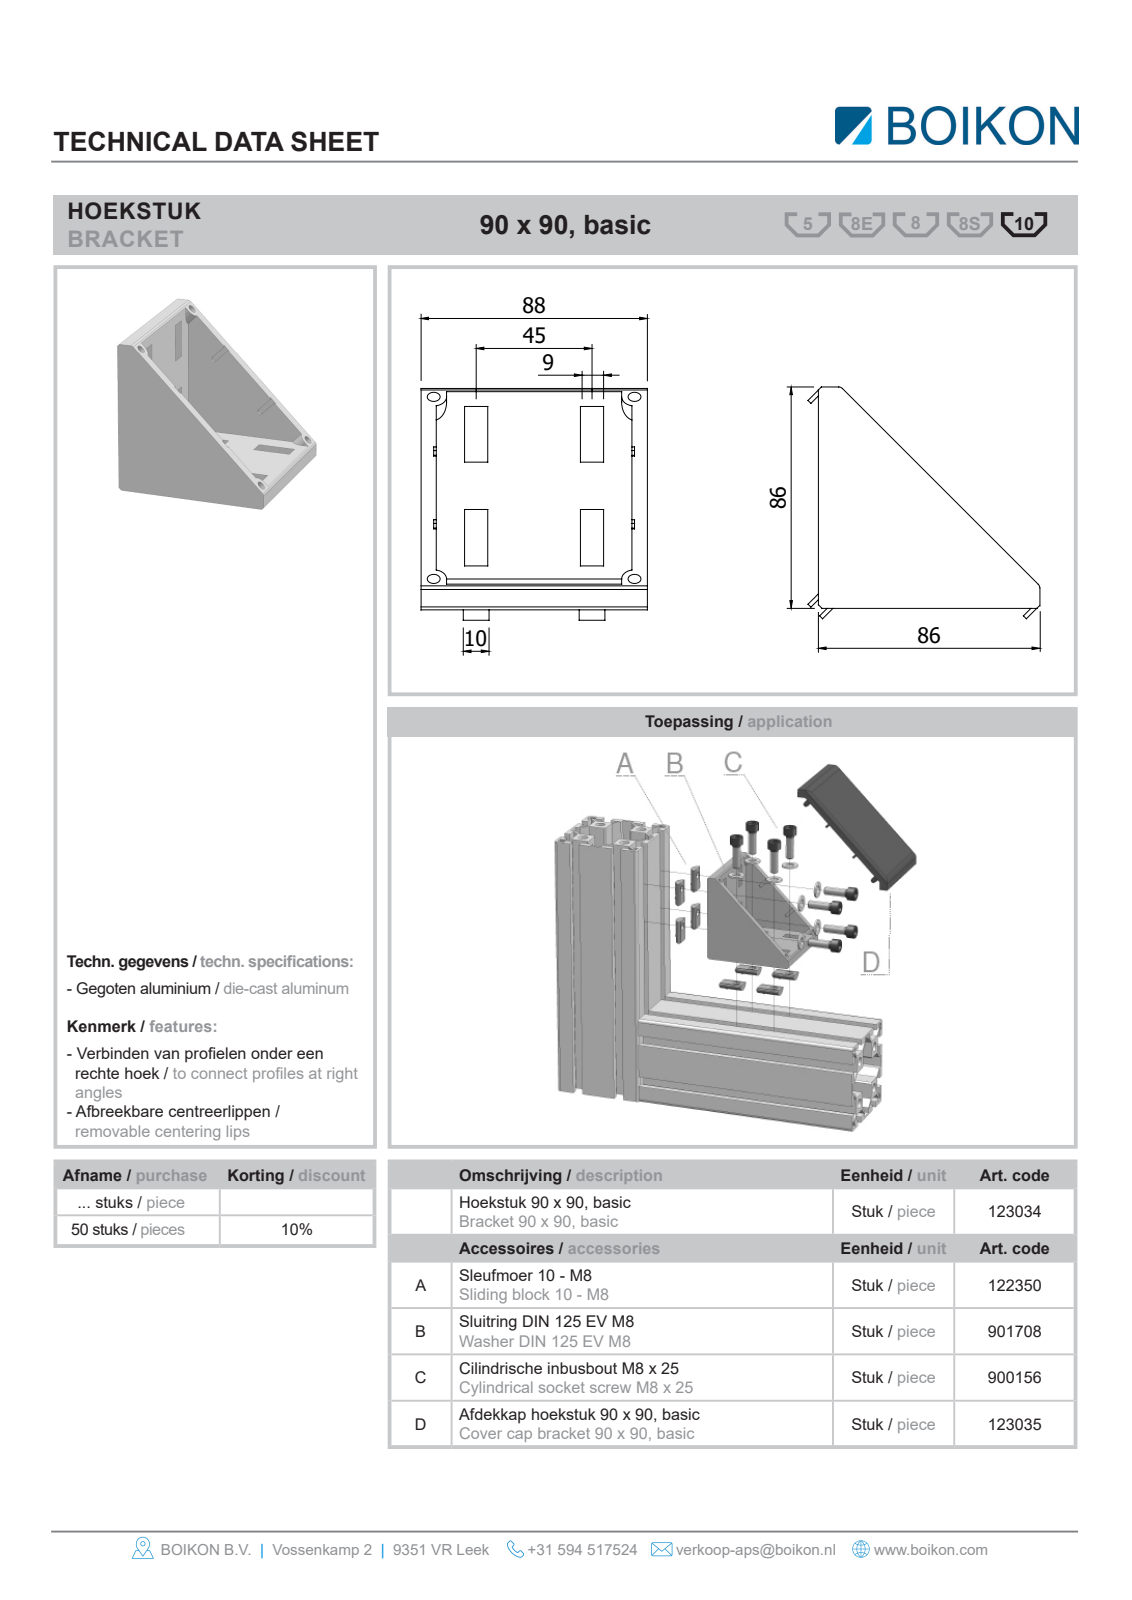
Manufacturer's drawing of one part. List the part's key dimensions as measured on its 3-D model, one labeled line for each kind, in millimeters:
Part name (STEP PRODUCT): Root; 123034HOEKSTUK 90X90 BASICBOIKON; 123035AFDEKKAP HOEKSTUK 90X90 BASICBOIKON; 900152Cil. inbusbout DIN 912 EV M8 x 20BOIKON0 (+2 more)
STEP written by: HiCAD 2013 1802.4 Build 509 (AUTOMOTIVE_DESIGN)
Units: millimetres
Bodies: 26 solids, 605 faces (455 planar, 102 cylindrical, 48 other)
Overall size (bounding box): 107.02 × 107.02 × 88
Volume: 191 586 mm³ · Surface area: 104 308 mm²
Round holes (diameter × count): ⌀8 ×8, ⌀8.4 ×8
Round bosses / shafts (diameter × count): ⌀16 ×8, ⌀13 ×8, ⌀6.47 ×8, ⌀5 ×4, ⌀7 ×1
Partial cylindrical surfaces — rounded edges, fillets, slot ends (radius × count): R1 ×4, R5 ×4, R8 ×4, R2 ×3, R1.5 ×2, R3 ×2, R6 ×2, R9 ×2
Main face-to-face distances: 5, 3, 6, 10, 82, 88, 76, 56, 71, 17
Hole centre spacings: 45, 39.5, 40.31, 59.88, 60.41
